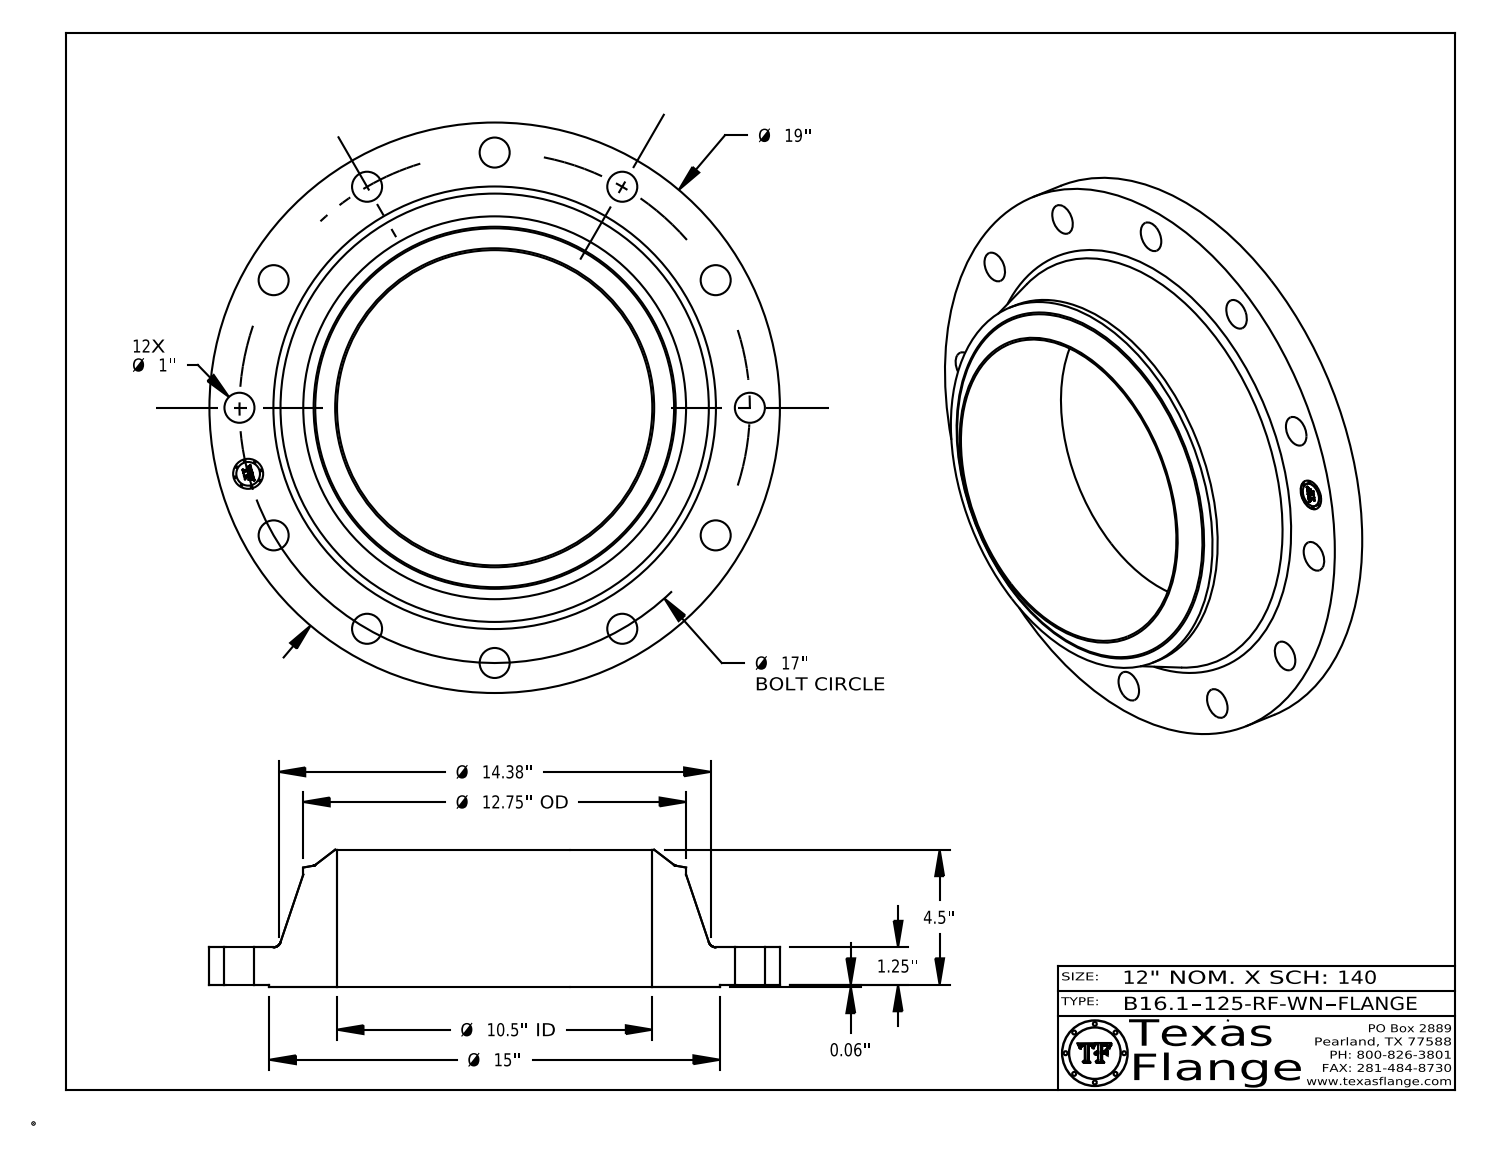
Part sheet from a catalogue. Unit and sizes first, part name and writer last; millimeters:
Units: millimetres
Overall size (bounding box): 482.6 × 482.6 × 115.9
Round holes (diameter × count): ⌀25.4 ×13, ⌀266.7 ×1
Round bosses / shafts (diameter × count): ⌀1.5 ×8, ⌀482.6 ×1, ⌀381 ×1, ⌀323.9 ×1, ⌀20 ×1
Main face-to-face distances: 31.8, 1.6, 33.4, 115.9, 114.3, 82.6, 0.4, 33, 31.4, 82.9
Hole centre spacings: 215.9, 417.1, 111.8, 305.3, 373.9, 111.8, 305.3, 373.9
Volume: 6 560 000 mm³ · Surface area: 476 400 mm²
Bodies: 1 solid, 431 faces (369 planar, 52 cylindrical, 10 other)
Part name (STEP PRODUCT): B16.1, Class 125-RF-WN
STEP written by: CATIA V5 STEP AP214 (AUTOMOTIVE_DESIGN)
